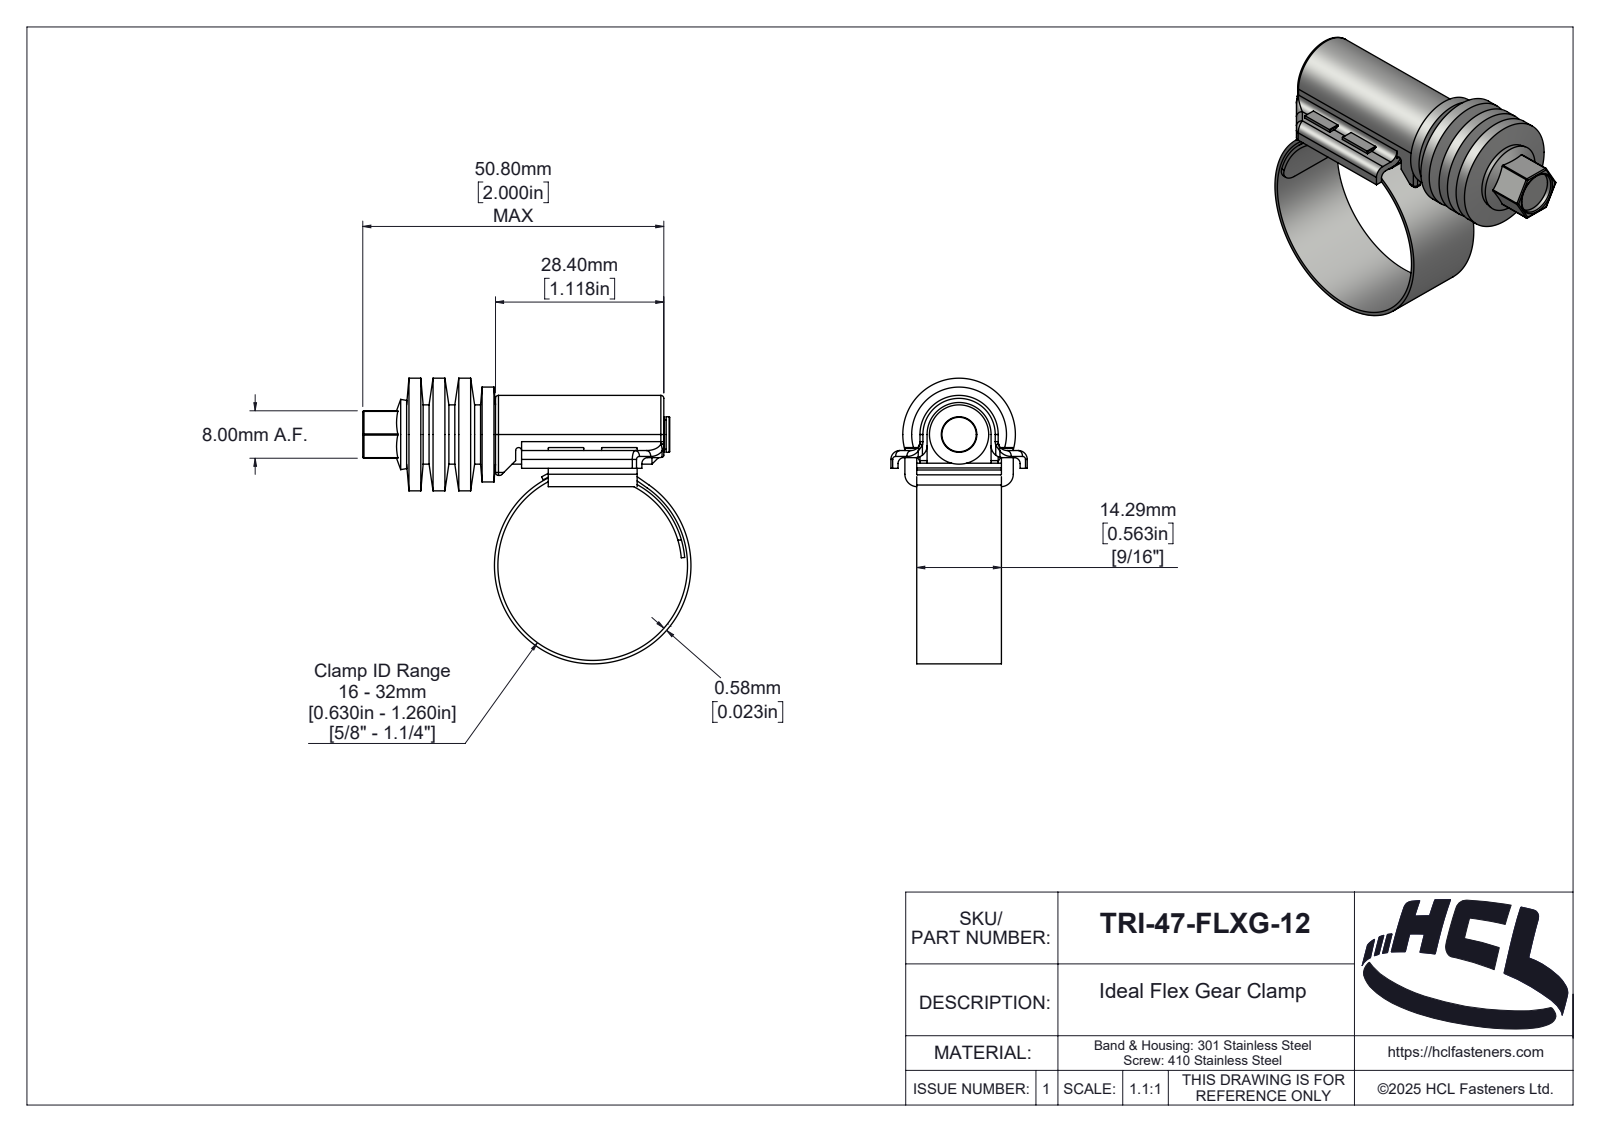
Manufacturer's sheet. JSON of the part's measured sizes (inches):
{"part_name": "TRI-47-FLXG-12", "step_written_by": "SolidWorks 2025 (AUTOMOTIVE_DESIGN)", "units": "inches", "bodies": {"solids": 4, "faces": 323, "planar": 88, "cylindrical": 139, "other": 96}, "overall_size": [2.18, 1.897, 0.906], "volume_in3": 0.53, "surface_area_in2": 16.2, "round_holes": [[0.276, 1], [1.26, 1]], "round_bosses_or_shafts": [[1.306, 1], [0.748, 1], [0.63, 1], [0.394, 1], [0.236, 1], [0.197, 1]], "partial_cylinders_radius": [[0.008, 12], [0.02, 9], [0.039, 8], [0.059, 4], [0.118, 4], [0.079, 3], [0.004, 2], [0.083, 2]], "face_to_face_distances": [0.079, 0.047, 0.193, 0.069, 0.494, 0.641, 0.24, 0.021, 0.541, 0.472]}
